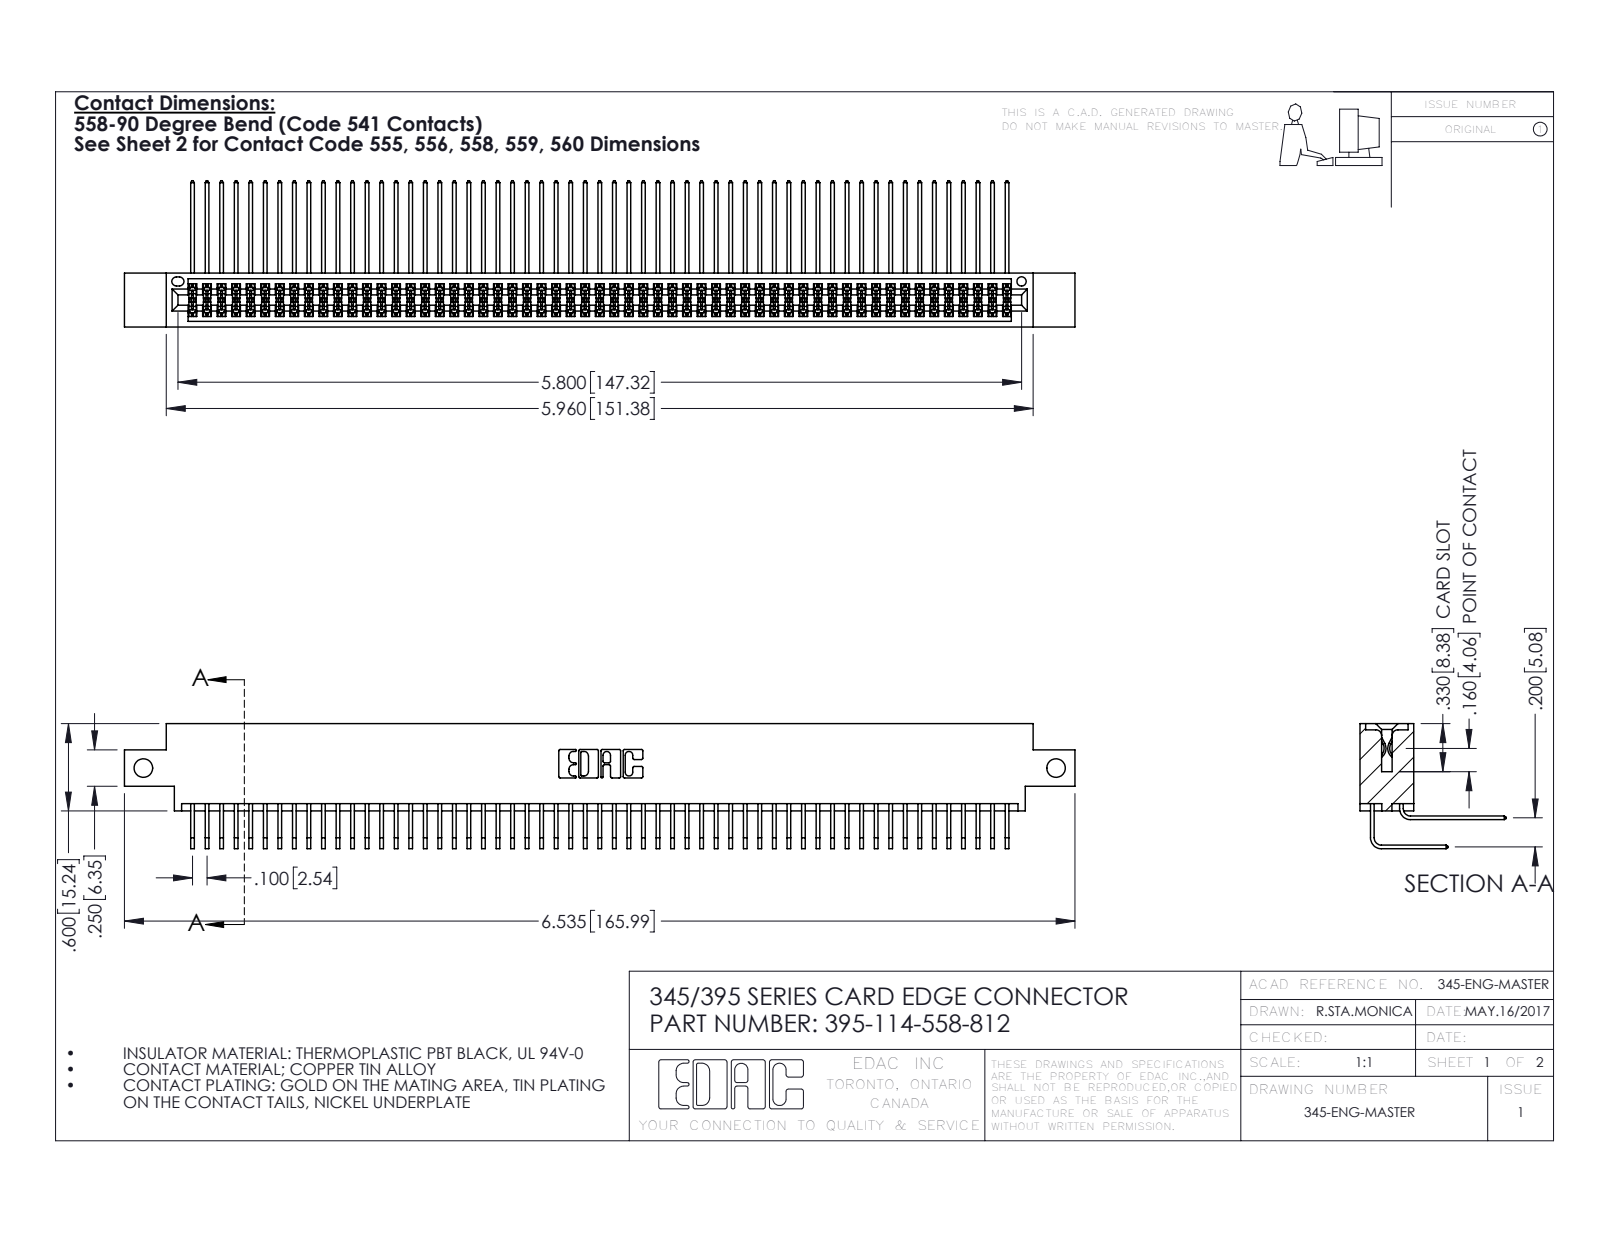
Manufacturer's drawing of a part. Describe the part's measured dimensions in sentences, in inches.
The part is named "395-114-558-812; 345-292-001_558 Tail - 2; 345 Part_0.170 Offset - Side Mount; 345-292-001_558 559 Tail - 1". Its 3-D file was written by "SolidWorks 2016 (CONFIG_CONTROL_DESIGN)". It is 115 solids with 6058 faces: 4074 planar, 1984 cylindrical and 0 other. Overall it measures 6.535 by 1.005 by 0.859 inches. Its volume is 1.02 cubic inches and its surface area 43.57 square inches. Round holes: 2 of diameter 0.128, 1 of diameter 0.064. Partial cylindrical surfaces (rounded edges, fillets, slot ends): 172 of radius 0.006, 22 of radius 0.01, 6 of radius 0.007, 6 of radius 0.031, 3 of radius 0.026, 2 of radius 0.014, 2 of radius 0.019, 2 of radius 0.022. The main face-to-face distances are 0.072, 0.298, 0.2, 0.37, 0.098, 0.272, 0.025, 0.225, 0.175, 0.025. The hole center spacings are 6.275.
